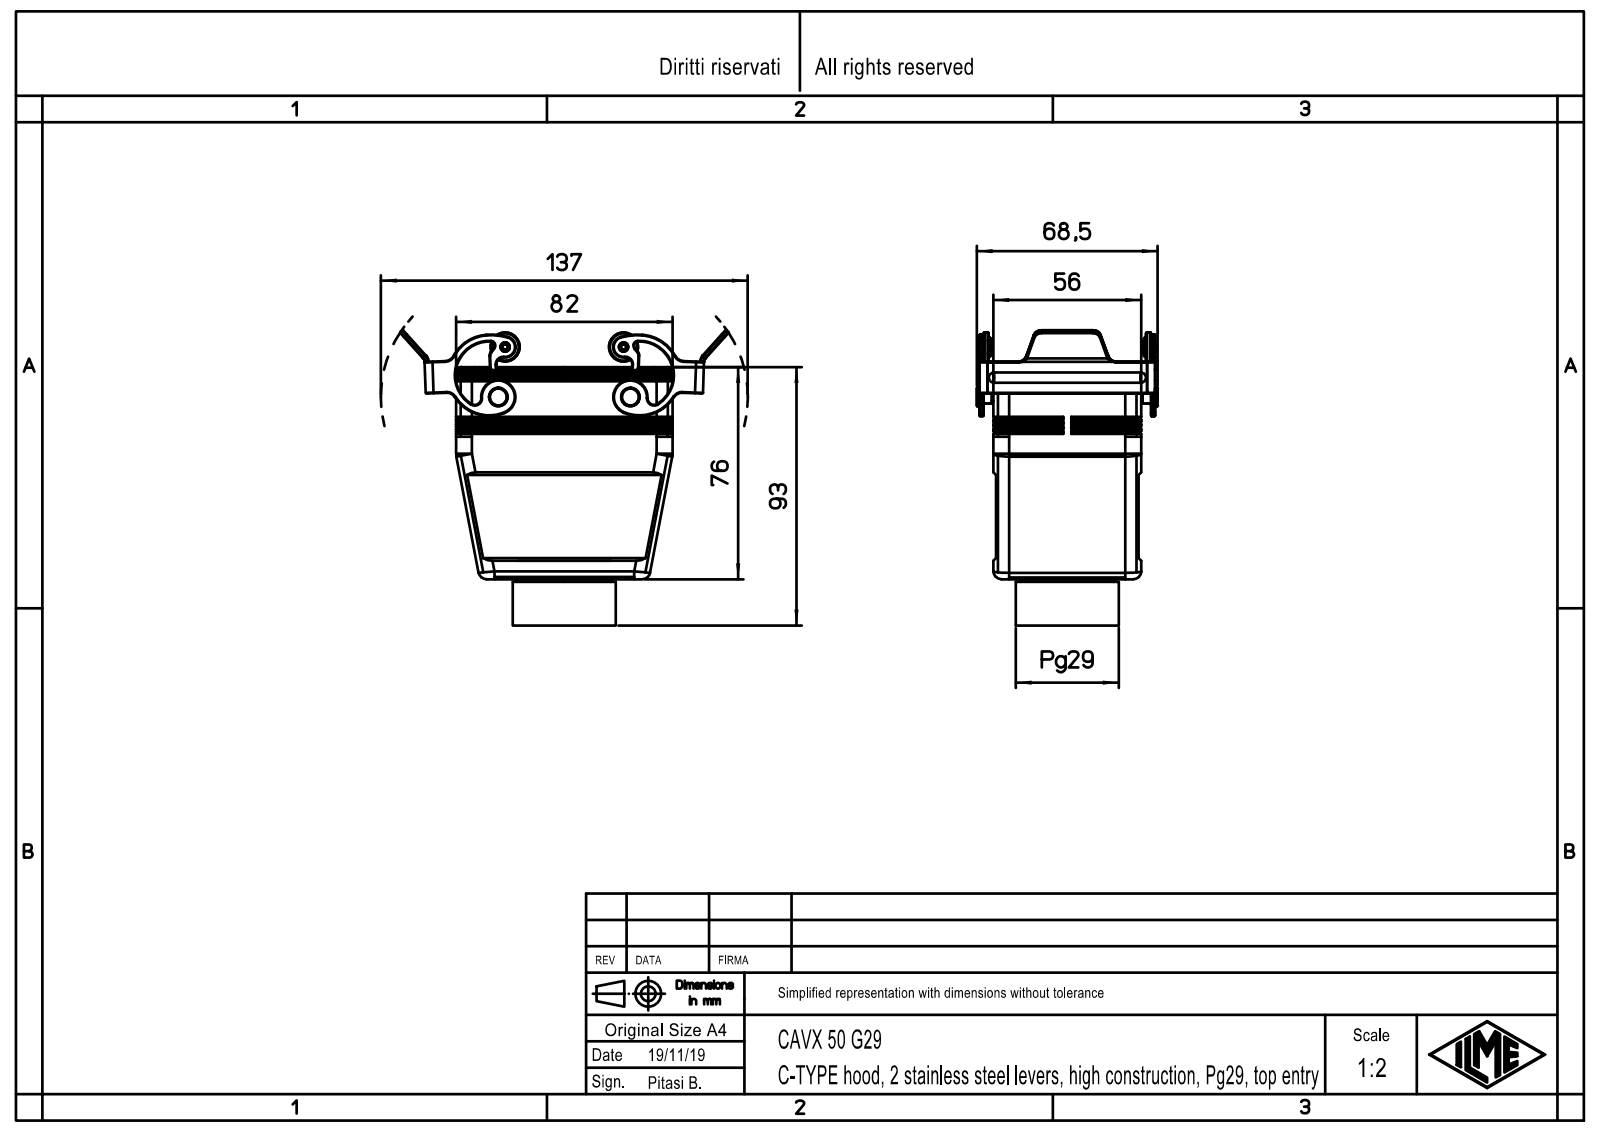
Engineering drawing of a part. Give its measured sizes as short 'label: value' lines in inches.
name: Leva.1; Leva; CAVX 50 G29
written by: Creo Elements/Direct Modeling 20.1B 02-Apr-2019 (C) Parametric Technology GmbH (AUTOMOTIVE_DESIGN)
unit: in
bodies: 3 solids, 752 faces (306 planar, 338 cylindrical, 108 other)
size: 4.834 × 4.419 × 2.697
volume: 5.61 in³; area: 102.8 in²
holes: 8× ⌀0.097, 8× ⌀0.138, 4× ⌀0.197, 2× ⌀0.047, 2× ⌀0.079, 2× ⌀0.122, 1× ⌀1.26, 1× ⌀1.427
bosses: 4× ⌀0.276, 4× ⌀0.189, 4× ⌀0.118, 2× ⌀0.433, 2× ⌀0.138, 1× ⌀1.575, 1× ⌀1.535, 1× ⌀1.39
rounds: 20× R0.118, 12× R0.079, 10× R0.236, 8× R0.157, 6× R0.059, 6× R0.138, 6× R0.217, 4× R0.098
face distances: 0.118, 2.087, 1.969, 0.079, 0.039, 2.165, 2.047, 0.059, 0.325, 2.205
hole spacings: 0.63, 0.945, 1.309, 1.519, 2.598, 2.674, 2.765, 0.315
